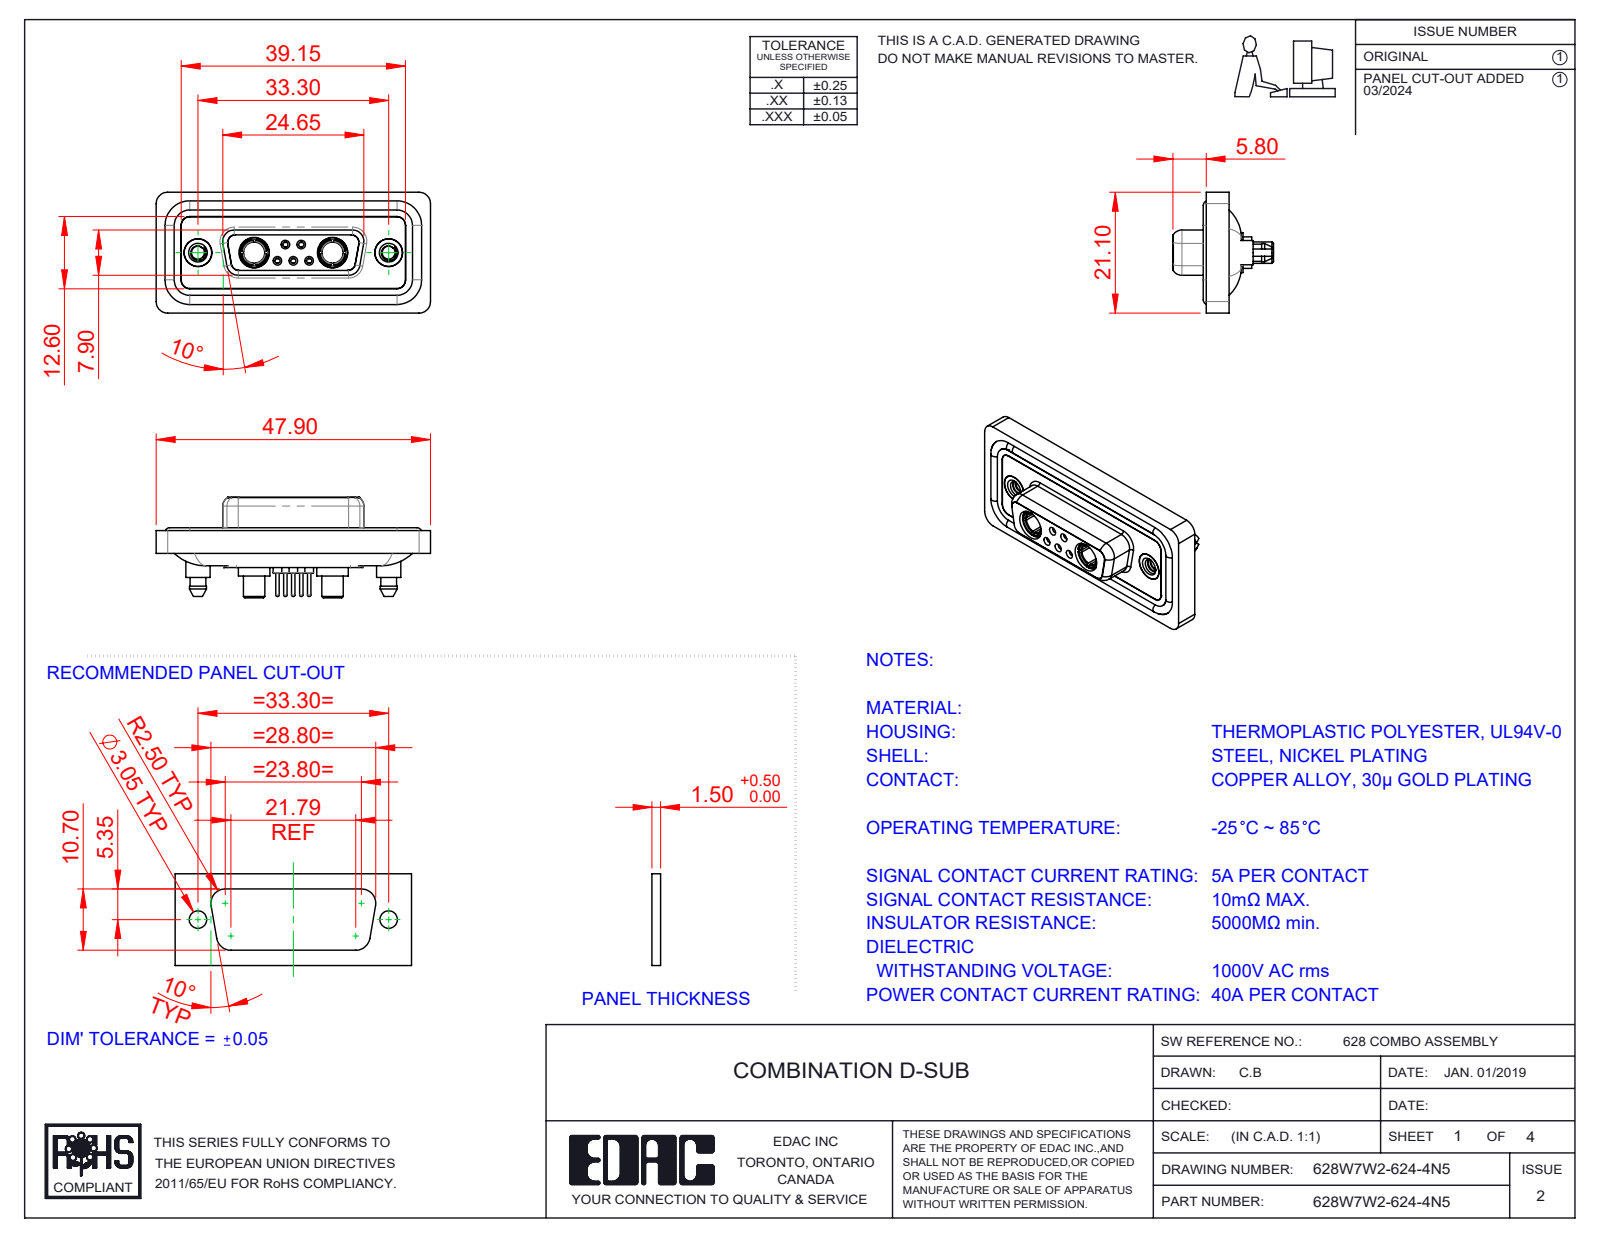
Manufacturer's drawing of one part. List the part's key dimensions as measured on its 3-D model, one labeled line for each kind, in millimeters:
Part name (STEP PRODUCT): 628Combo Housing_7W2; 628Combo Shell Front_15 Contacts; 628Combo Contact Row 1_24; 628W7W2-624-4N5 (+5 more)
STEP written by: SolidWorks 2023 (CONFIG_CONTROL_DESIGN)
Units: millimetres
Bodies: 16 solids, 859 faces (254 planar, 361 cylindrical, 244 other)
Overall size (bounding box): 47.9 × 21.1 × 17.55
Volume: 6 248 mm³ · Surface area: 10 240 mm²
Round holes (diameter × count): ⌀0.9 ×5, ⌀1.1 ×5, ⌀1.5 ×5, ⌀2 ×5, ⌀4.85 ×4, ⌀1.6 ×3, ⌀1.7 ×2, ⌀2.26 ×2, ⌀3.7 ×2, ⌀4 ×2, ⌀4.05 ×2, ⌀5 ×2
Round bosses / shafts (diameter × count): ⌀1.6 ×6, ⌀2.2 ×5, ⌀0.6 ×5, ⌀5.5 ×2, ⌀5.4 ×2, ⌀5.2 ×2, ⌀4.96 ×2, ⌀4.95 ×2
Partial cylindrical surfaces — rounded edges, fillets, slot ends (radius × count): R1.5 ×24, R2 ×20, R1.35 ×12, R1.6 ×10, R0.25 ×4, R0.5 ×4, R0.6 ×4, R0.65 ×4
Main face-to-face distances: 0.4, 1.8, 1.6, 0.5, 2.9, 1.1, 7.45, 5.65, 6.6, 7.05
Hole centre spacings: 3.16, 2.77, 9.8, 23.5, 4.31, 4.33, 5.03, 5.04
